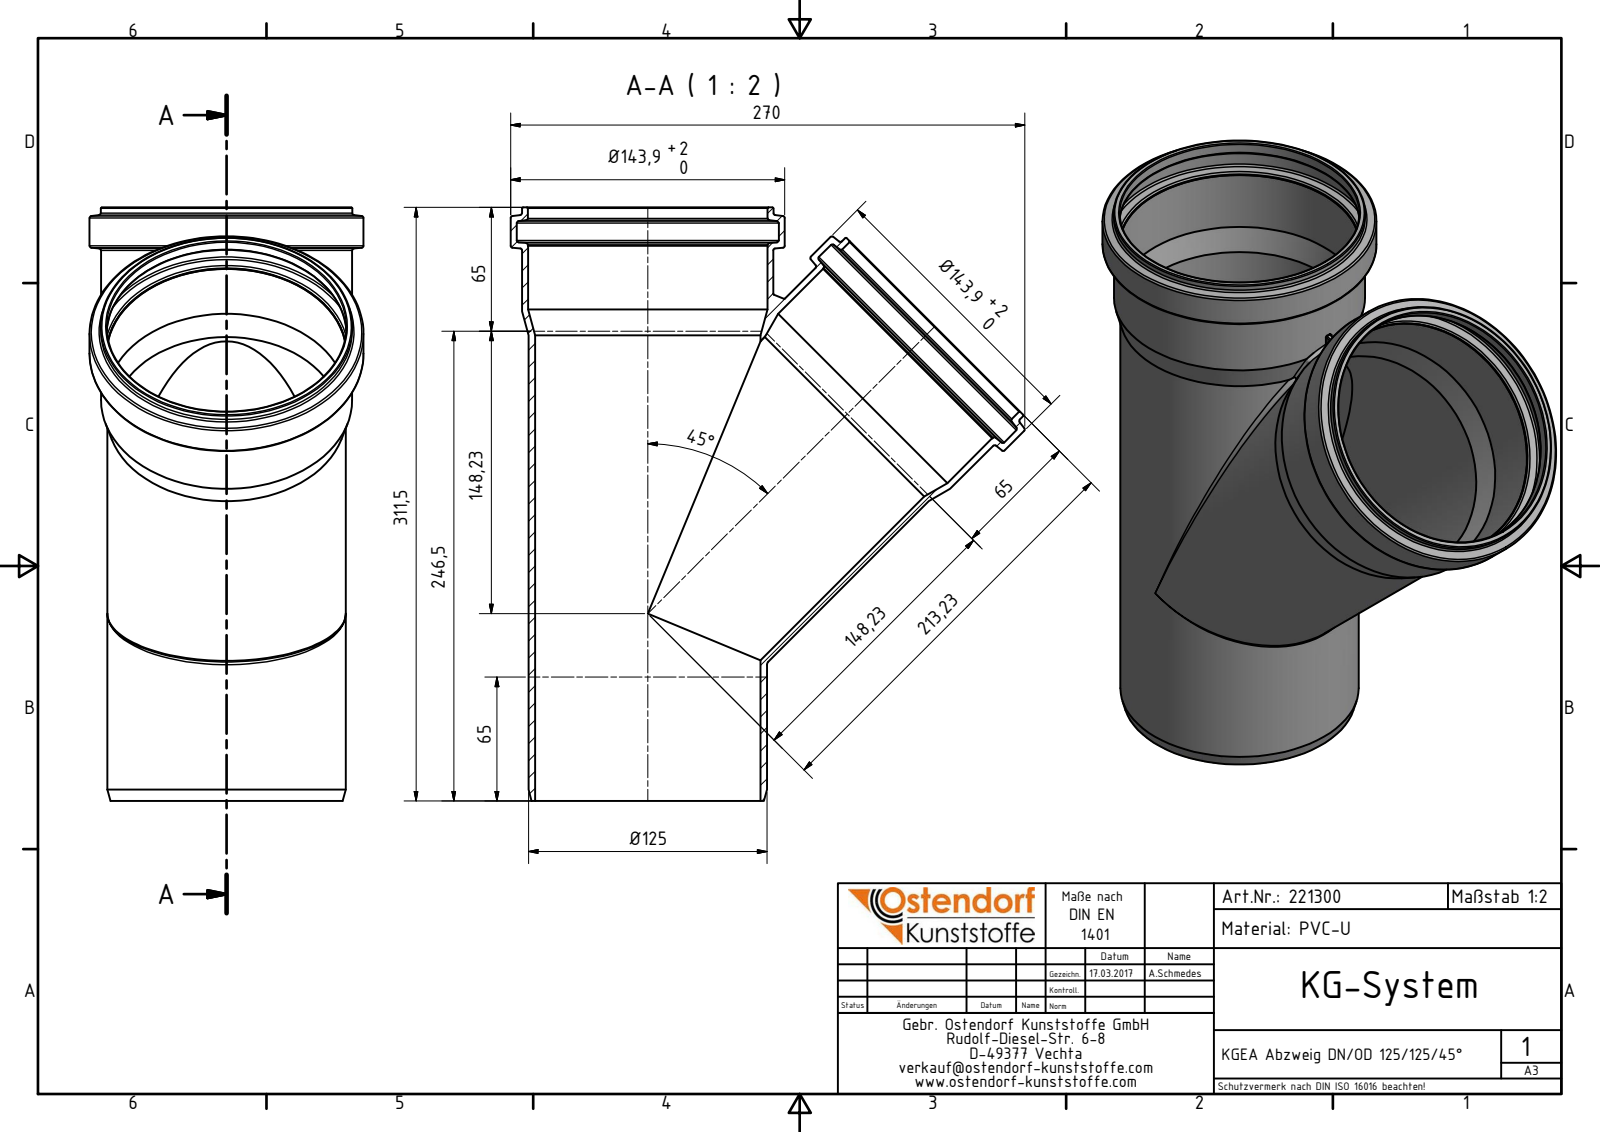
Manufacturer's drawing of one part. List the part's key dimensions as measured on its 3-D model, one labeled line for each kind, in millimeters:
Part name (STEP PRODUCT): 221300 KGEA Abzweig DN_OD 125_125_45°
STEP written by: Autodesk Inventor 2016 (AUTOMOTIVE_DESIGN)
Units: millimetres
Bodies: 1 solid, 78 faces (8 planar, 24 cylindrical, 46 other)
Overall size (bounding box): 311.5 × 270 × 143.9
Volume: 565 818 mm³ · Surface area: 343 748 mm²
Round holes (diameter × count): ⌀118.4 ×2, ⌀125.7 ×2, ⌀125.9 ×2, ⌀137.7 ×2
Round bosses / shafts (diameter × count): ⌀143.9 ×2, ⌀132.1 ×2, ⌀131.9 ×2, ⌀125.2 ×2
Partial cylindrical surfaces — rounded edges, fillets, slot ends (radius × count): R0.5 ×6
Main face-to-face distances: 311.5, 20.17, 291.33, 3
